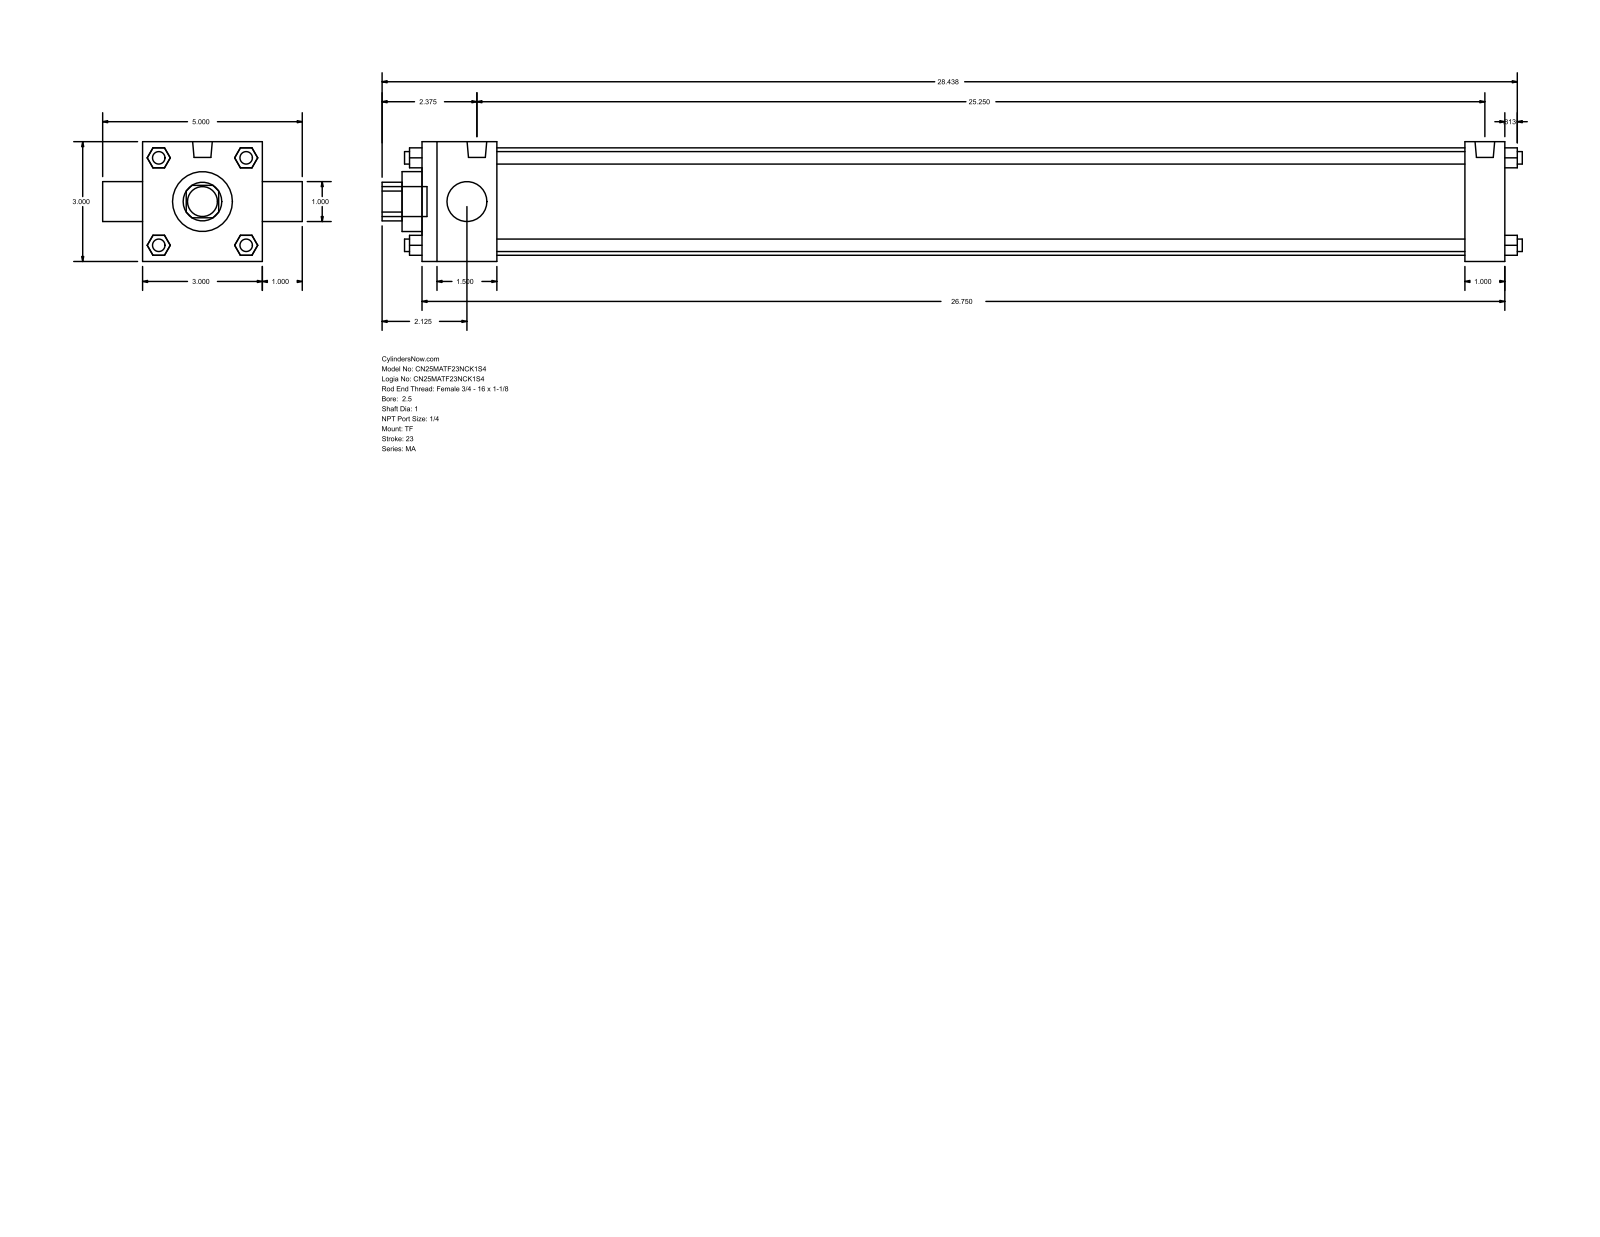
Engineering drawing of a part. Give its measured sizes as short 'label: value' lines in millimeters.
name: MA_TF__0250_1
written by: GSSL Pune (CONFIG_CONTROL_DESIGN)
unit: mm
bodies: 0 solids, 120 faces (92 planar, 28 cylindrical, 0 other)
size: 725.49 × 127 × 76.2
holes: 2× ⌀25.4, 1× ⌀38.1, 1× ⌀68.33
bosses: 7× ⌀7.94, 2× ⌀12.49, 1× ⌀19.05
rounds: 1× R12.29
face distances: 76.2, 688.98, 25.4, 12.7, 47.63, 663.58, 615.95, 641.35, 101.6, 27.81
